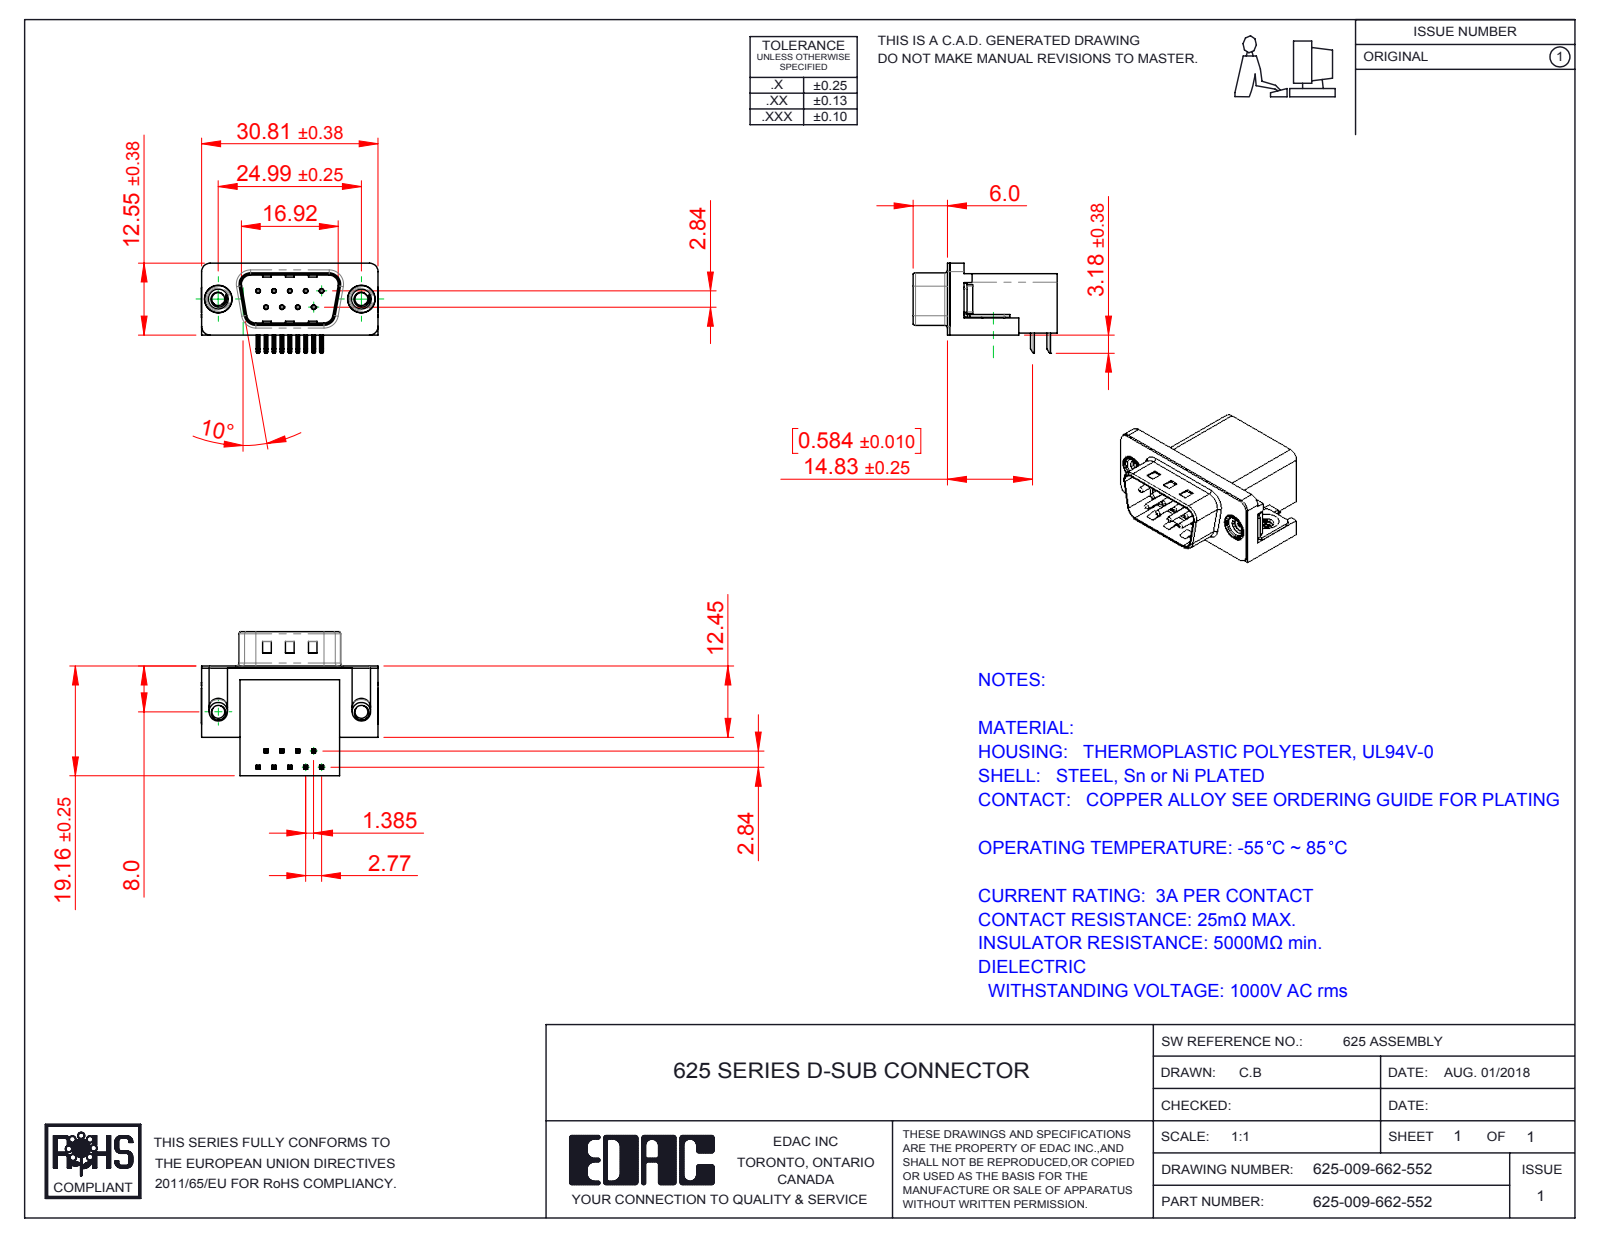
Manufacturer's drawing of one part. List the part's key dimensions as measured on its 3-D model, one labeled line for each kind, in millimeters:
Part name (STEP PRODUCT): 625 4-40 Threaded Board Mount; 625 Shell_9 Socket; 625 Contact Top; 625 Contact Bottom (+3 more)
STEP written by: SolidWorks 2016 (CONFIG_CONTROL_DESIGN)
Units: millimetres
Bodies: 15 solids, 1025 faces (575 planar, 329 cylindrical, 121 other)
Overall size (bounding box): 30.89 × 25.16 × 15.73
Volume: 4 488 mm³ · Surface area: 5 031 mm²
Round holes (diameter × count): ⌀0.35 ×9, ⌀0.8 ×9, ⌀2.26 ×4, ⌀4 ×2, ⌀4.8 ×2, ⌀5 ×2
Round bosses / shafts (diameter × count): ⌀0.75 ×9, ⌀4.9 ×2, ⌀4.75 ×2, ⌀3.9 ×2, ⌀3.26 ×2
Partial cylindrical surfaces — rounded edges, fillets, slot ends (radius × count): R0.25 ×44, R0.12 ×18, R1 ×16, R0.5 ×9, R1.5 ×8, R1.6 ×8, R0.9 ×4, R2 ×4
Main face-to-face distances: 0.4, 10.34, 18.76, 19.16, 2.9, 16.26, 2.5, 0.35, 10.69, 6.7
Hole centre spacings: 3.16, 2.77, 5.54, 5.03, 5.04, 8.31, 7.48, 7.49
